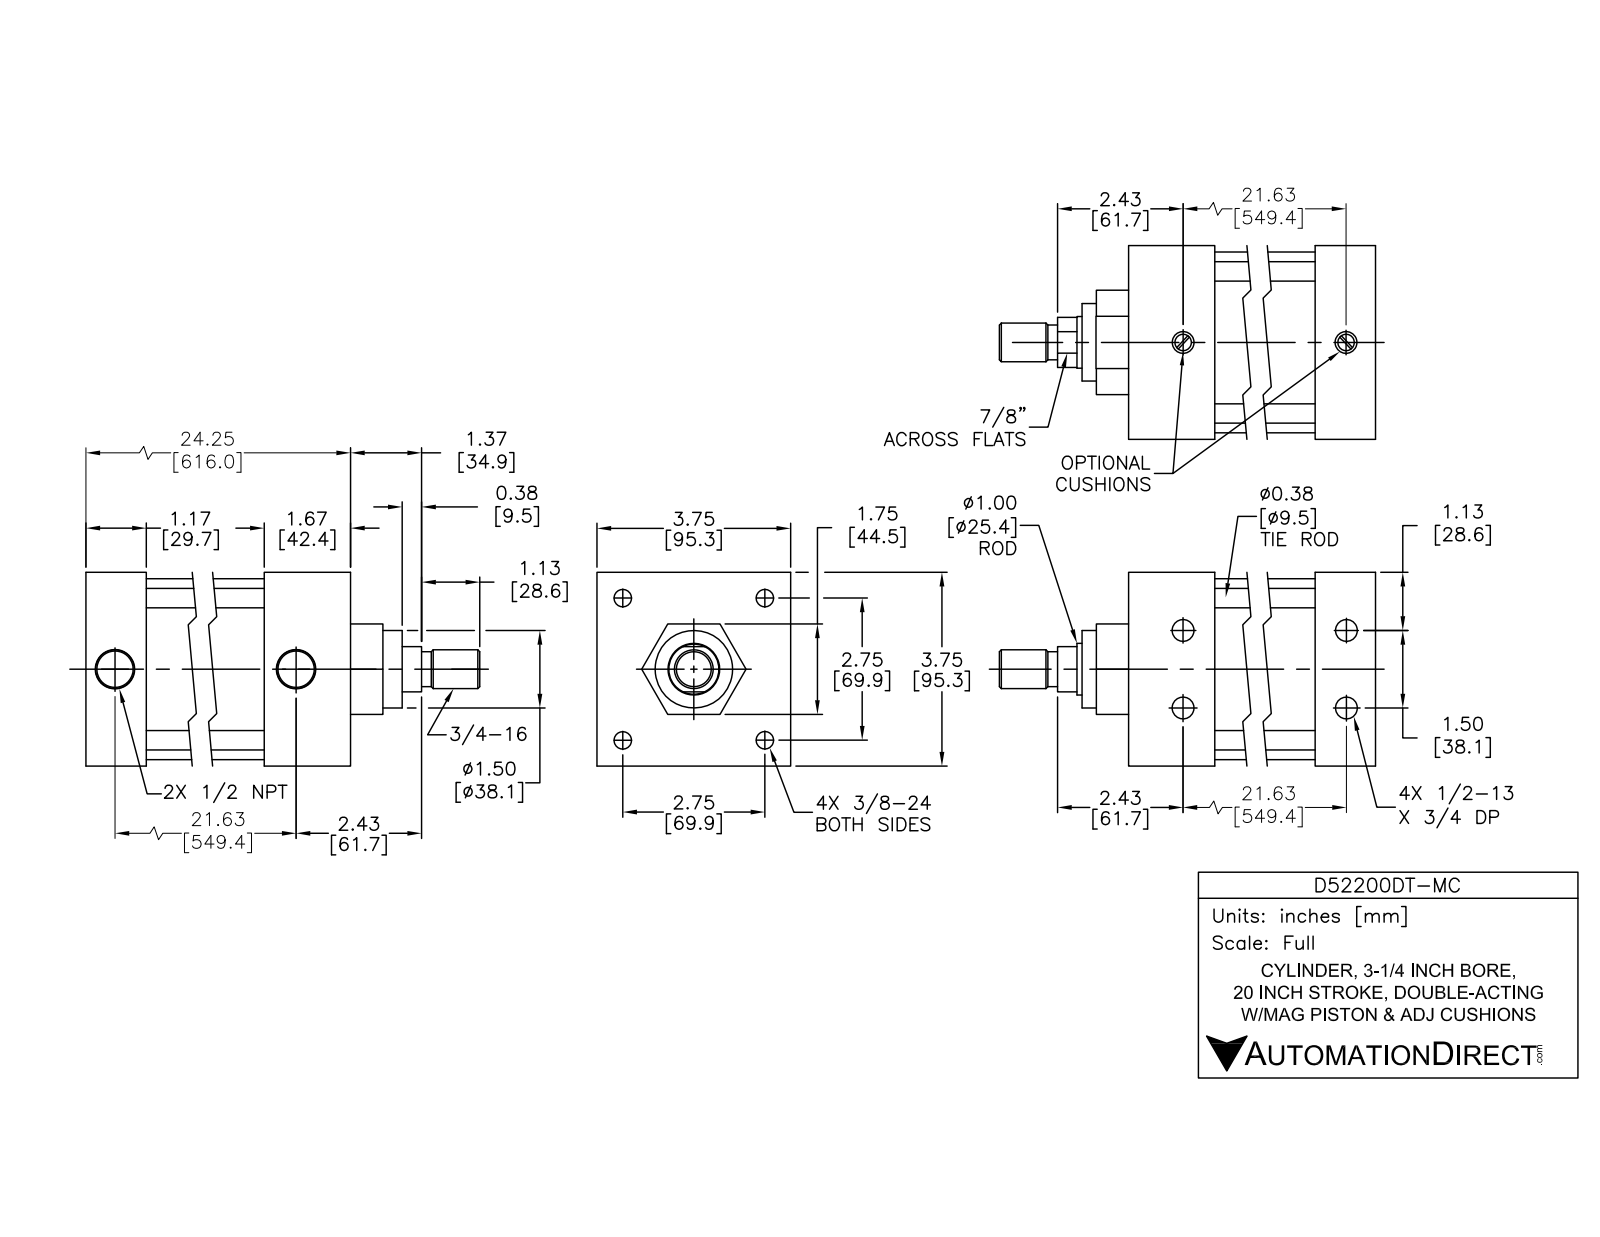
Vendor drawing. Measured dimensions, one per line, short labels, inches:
name: D52200DT-M BODY; D52200DT-MC; D52200DT-M PISTON
written by: SolidWorks 2015 (AUTOMOTIVE_DESIGN)
unit: in
bodies: 12 solids, 303 faces (99 planar, 114 cylindrical, 90 other)
size: 26.745 × 3.75 × 3.75
volume: 103.2 in³; area: 809.3 in²
holes: 4× ⌀0.33, 4× ⌀0.406, 4× ⌀0.417, 4× ⌀0.625, 2× ⌀0.5, 2× ⌀0.766, 1× ⌀1, 1× ⌀1.003, 1× ⌀3.25
bosses: 4× ⌀0.609, 4× ⌀0.375, 4× ⌀0.34, 1× ⌀3.5, 1× ⌀3.247, 1× ⌀1.75, 1× ⌀0.997, 1× ⌀0.97
rounds: 4× R0.375
face distances: 3.75, 0.08, 21.326, 24.246, 1.75, 22.997, 1.249, 21.751, 1.246, 2.495
hole spacings: 1.95, 2.758, 0.75, 0.76, 1.5, 3.901, 22.5, 22.517
